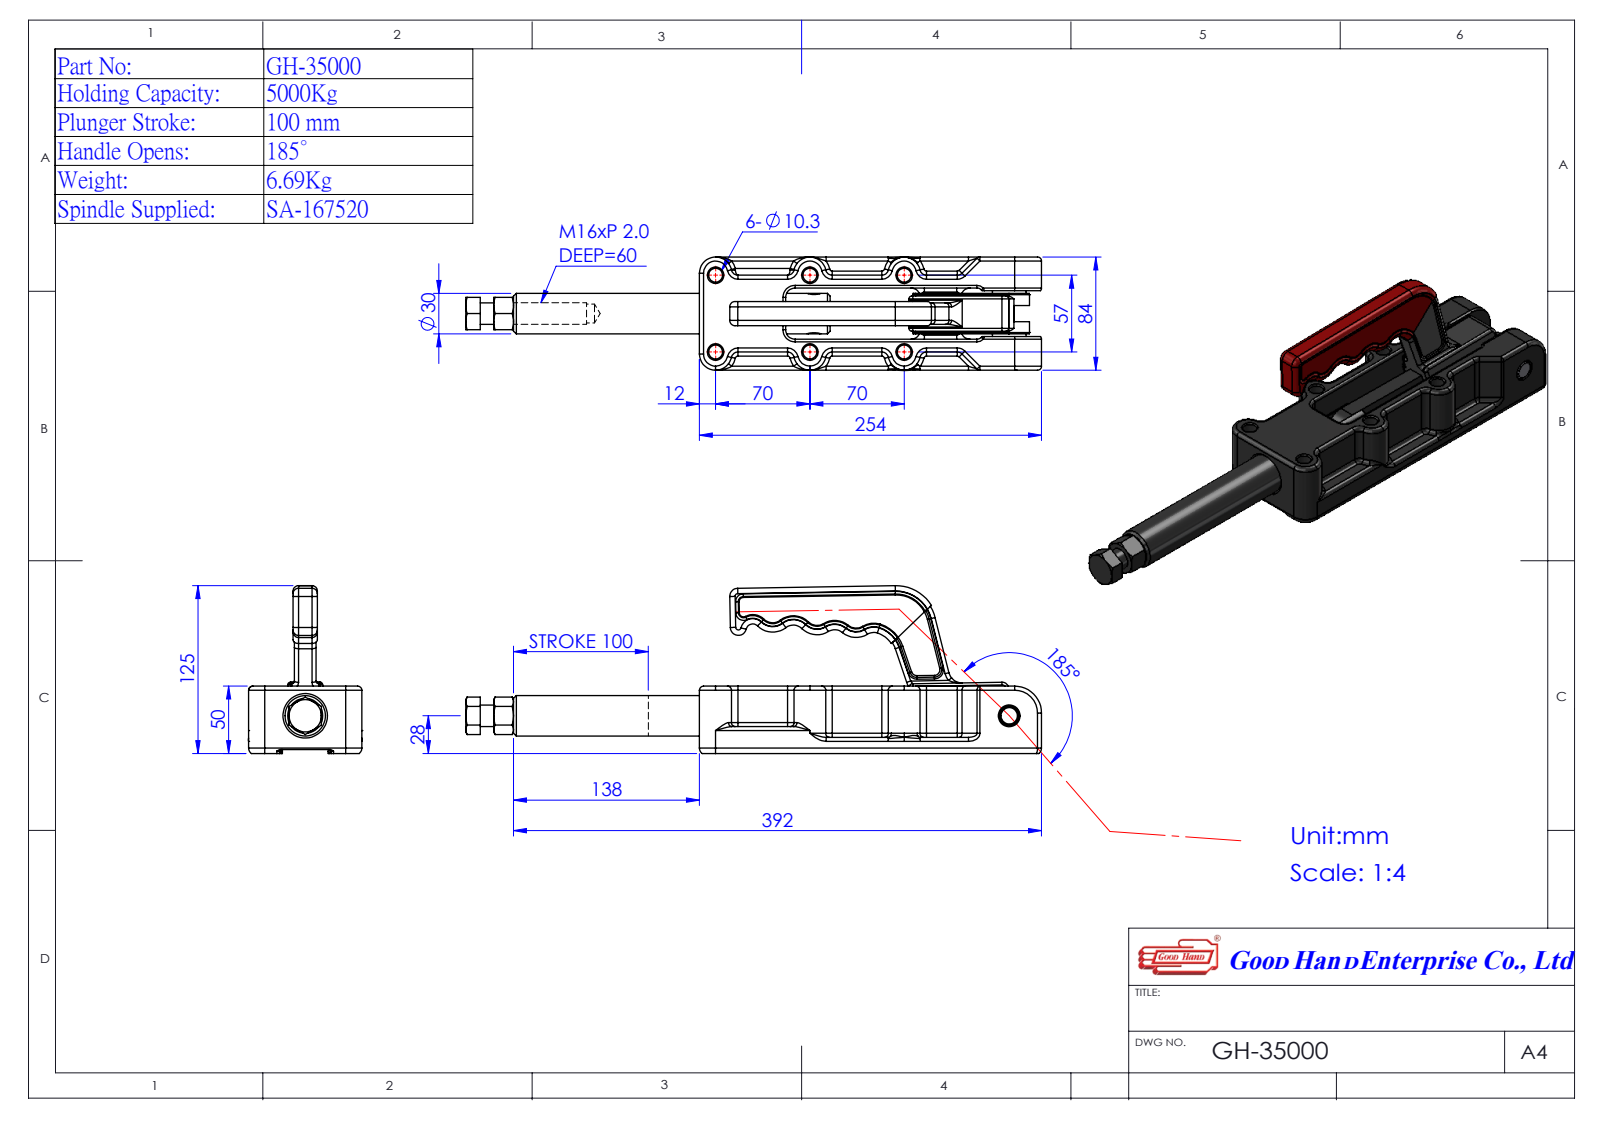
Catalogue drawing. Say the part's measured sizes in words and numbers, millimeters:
The part is named "GH-35000(簡化); 43500005-1^GH-35000(簡化); Group5^GH-35000(簡化); Group4^GH-35000(簡化) (+2 more)". Its 3-D file was written by "SolidWorks 2016 (AUTOMOTIVE_DESIGN)". It is 5 solids with 352 faces: 103 planar, 117 cylindrical and 132 other. Overall it measures 453.67 by 124.61 by 84 millimeters. Its volume is 878 243 cubic millimeters and its surface area 178 576 square millimeters. Round holes: 6 of diameter 10.3, 2 of diameter 8, 1 of diameter 11, 1 of diameter 14, 1 of diameter 30. Round bosses or shafts: 1 of diameter 24, 1 of diameter 16. Partial cylindrical surfaces (rounded edges, fillets, slot ends): 15 of radius 2, 14 of radius 5, 8 of radius 3, 6 of radius 12, 4 of radius 1, 4 of radius 4, 3 of radius 9, 3 of radius 16. The main face-to-face distances are 23, 50, 34, 13.5, 38, 61, 27, 25, 2, 57. The hole center spacings are 70, 90.27, 57, 140, 151.16, 53, 92, 144.99.
